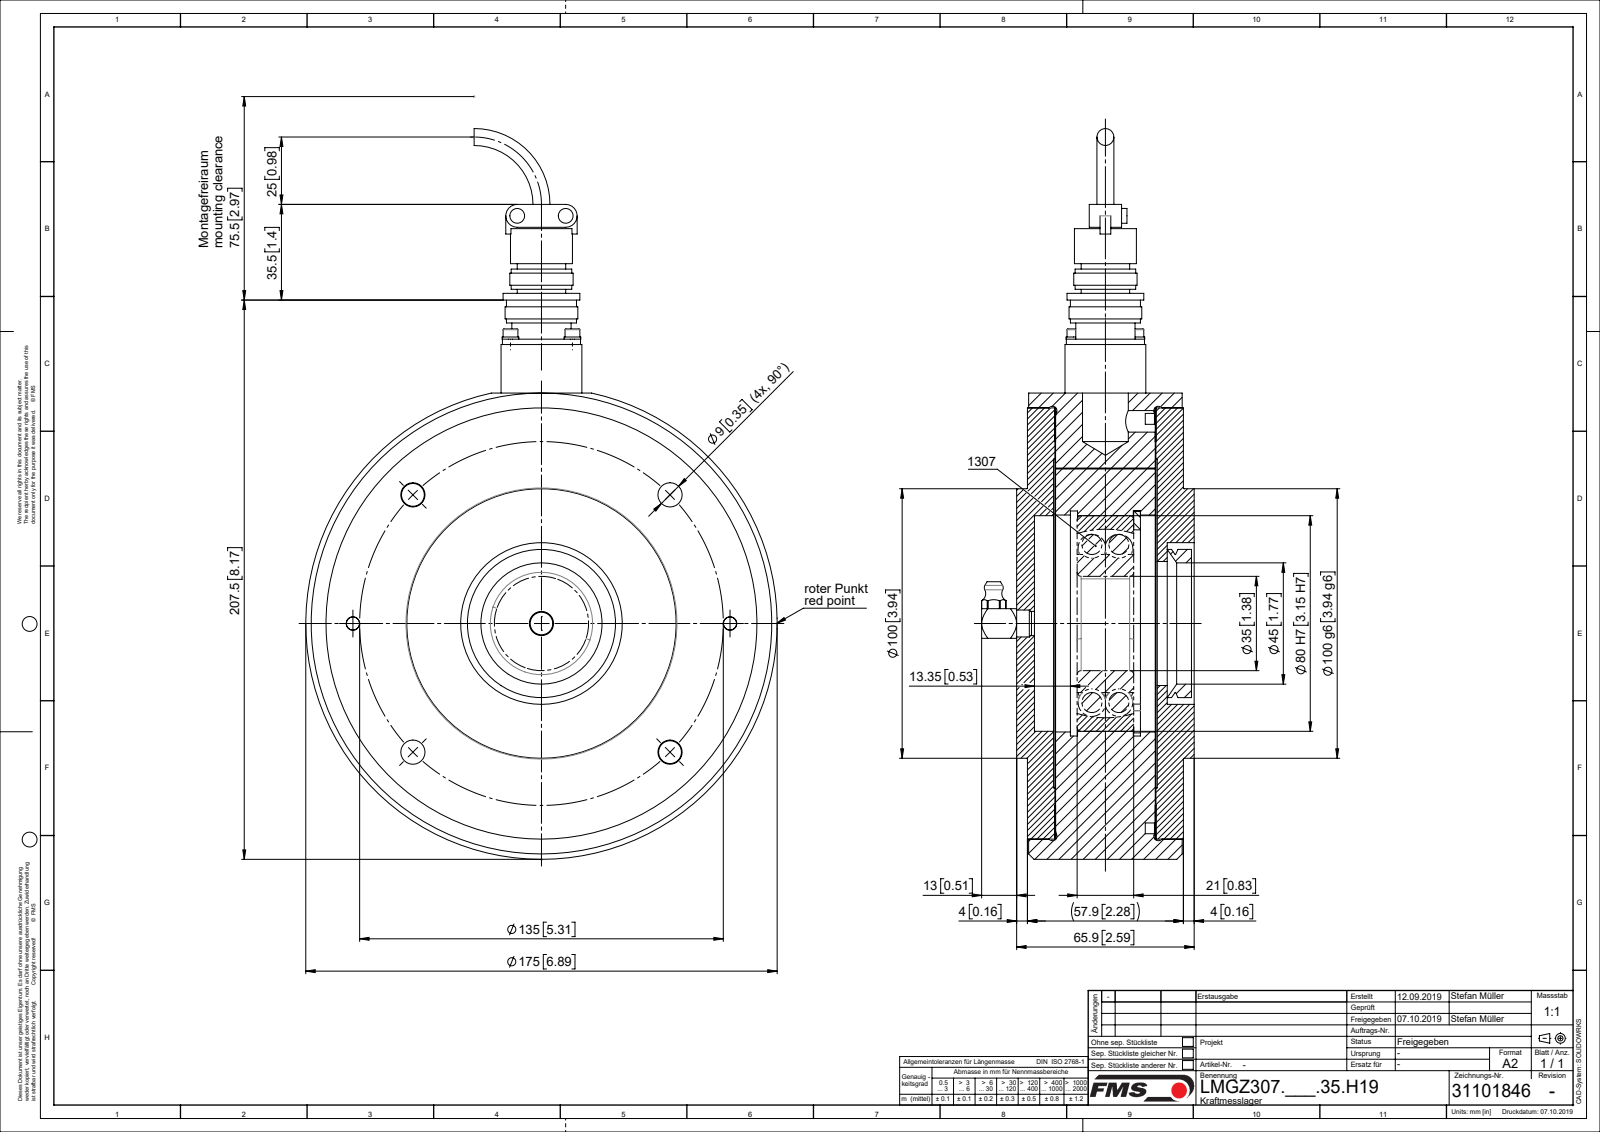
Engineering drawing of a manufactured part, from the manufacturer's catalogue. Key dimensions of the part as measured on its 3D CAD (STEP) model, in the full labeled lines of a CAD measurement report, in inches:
Part name (STEP PRODUCT): ZEICHNUNG10; L50006; L4857104; TEIL1 (+8 more)
STEP written by: Mechanical Desktop 2009 (CONFIG_CONTROL_DESIGN)
Units: inches
Bodies: 23 solids, 423 faces (112 planar, 241 cylindrical, 70 other)
Overall size (bounding box): 12.5 × 10.675 × 4.693
Volume: 78.48 in³ · Surface area: 421.2 in²
Round holes (diameter × count): ⌀0.354 ×5, ⌀0.102 ×4, ⌀0.126 ×4, ⌀0.134 ×4, ⌀0.197 ×2, ⌀0.26 ×2, ⌀0.335 ×2, ⌀0.433 ×2, ⌀0.315 ×1, ⌀0.394 ×1, ⌀0.906 ×1, ⌀1.378 ×1
Round bosses / shafts (diameter × count): ⌀0.217 ×6, ⌀0.244 ×4, ⌀0.118 ×4, ⌀0.098 ×4, ⌀0.394 ×3, ⌀0.236 ×2, ⌀6.89 ×1, ⌀6.299 ×1
Partial cylindrical surfaces — rounded edges, fillets, slot ends (radius × count): R0.167 ×2, R0.295 ×2
Main face-to-face distances: 1.467, 0.402, 0.411, 1.868, 1.878, 1.457, 0.02, 1.496, 0.382, 1.898
Hole centre spacings: 0.64, 0.906, 1.918, 2.074, 2.657, 3.758, 4.549, 5.002
